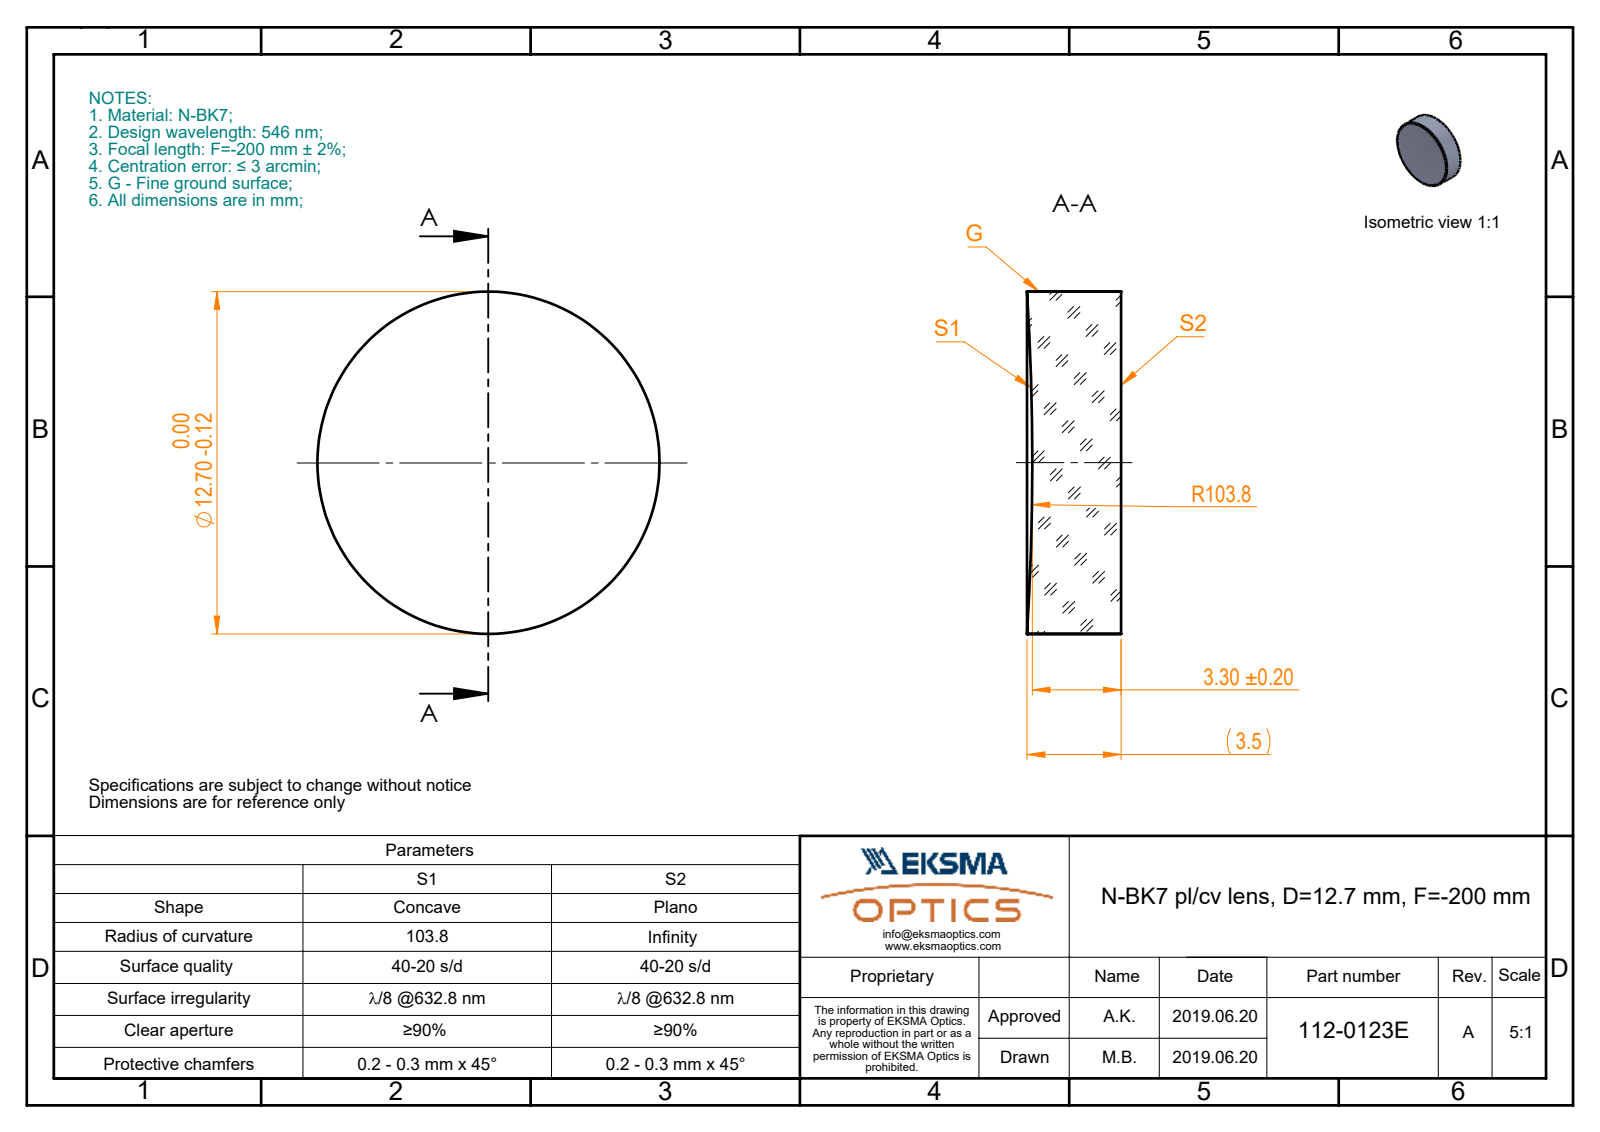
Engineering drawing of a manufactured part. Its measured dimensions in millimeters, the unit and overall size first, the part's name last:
Units: millimetres
Overall size (bounding box): 12.7 × 12.7 × 3.5
Round bosses / shafts (diameter × count): ⌀12.7 ×1
Volume: 430 mm³ · Surface area: 393 mm²
Bodies: 1 solid, 5 faces (1 planar, 2 cylindrical, 2 other)
Part name (STEP PRODUCT): 112-0123E BK7 pl-cv 12.7 F-200
STEP written by: SolidWorks 2017 (CONFIG_CONTROL_DESIGN)
